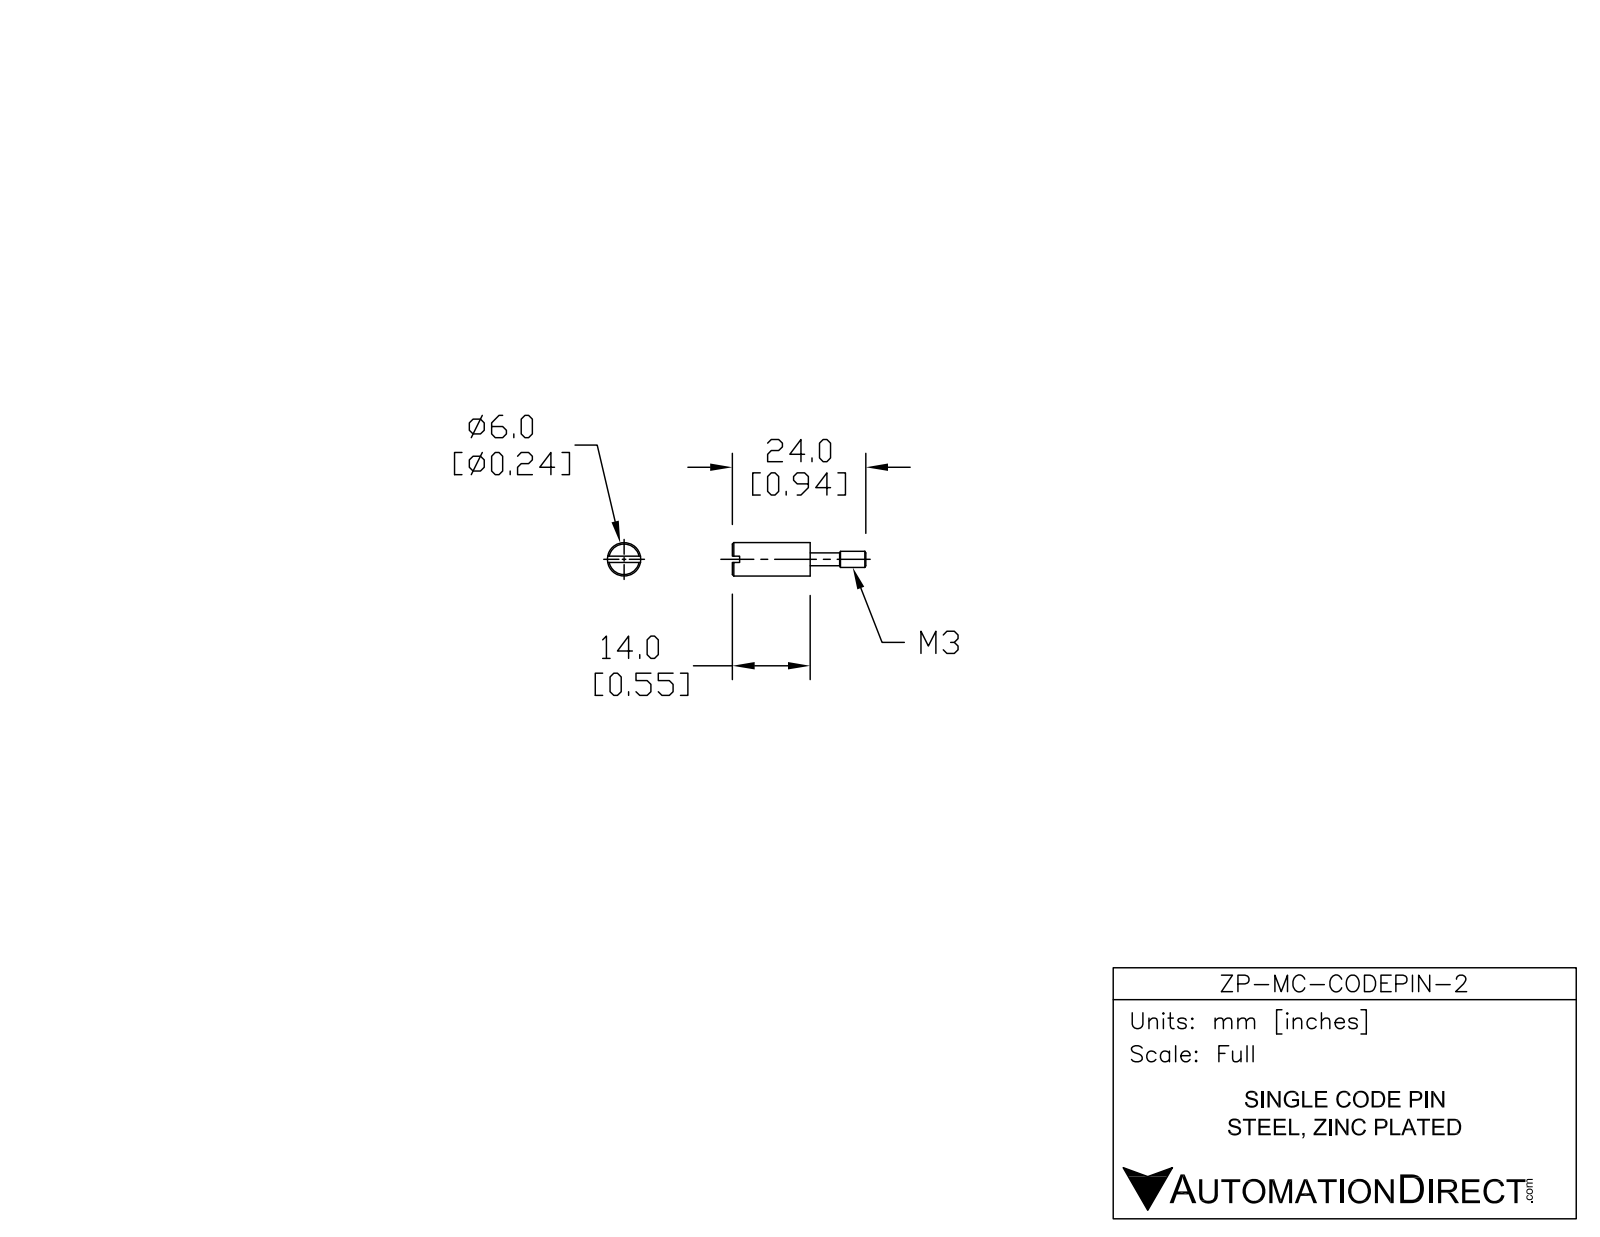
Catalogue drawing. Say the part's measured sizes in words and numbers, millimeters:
The part is named "ZP-MC-CODEPIN-2". Its 3-D file was written by "SolidWorks 2014 (AUTOMOTIVE_DESIGN)". It is 1 solid with 19 faces: 7 planar, 6 cylindrical and 6 other. Overall it measures 24 by 6 by 6 millimeters. Its volume is 439 cubic millimeters and its surface area 414 square millimeters. Round bosses or shafts: 1 of diameter 6, 1 of diameter 2.9, 1 of diameter 2.32. The main face-to-face distances are 14, 1.14, 12.69, 1.31, 10, 22.69, 24.
